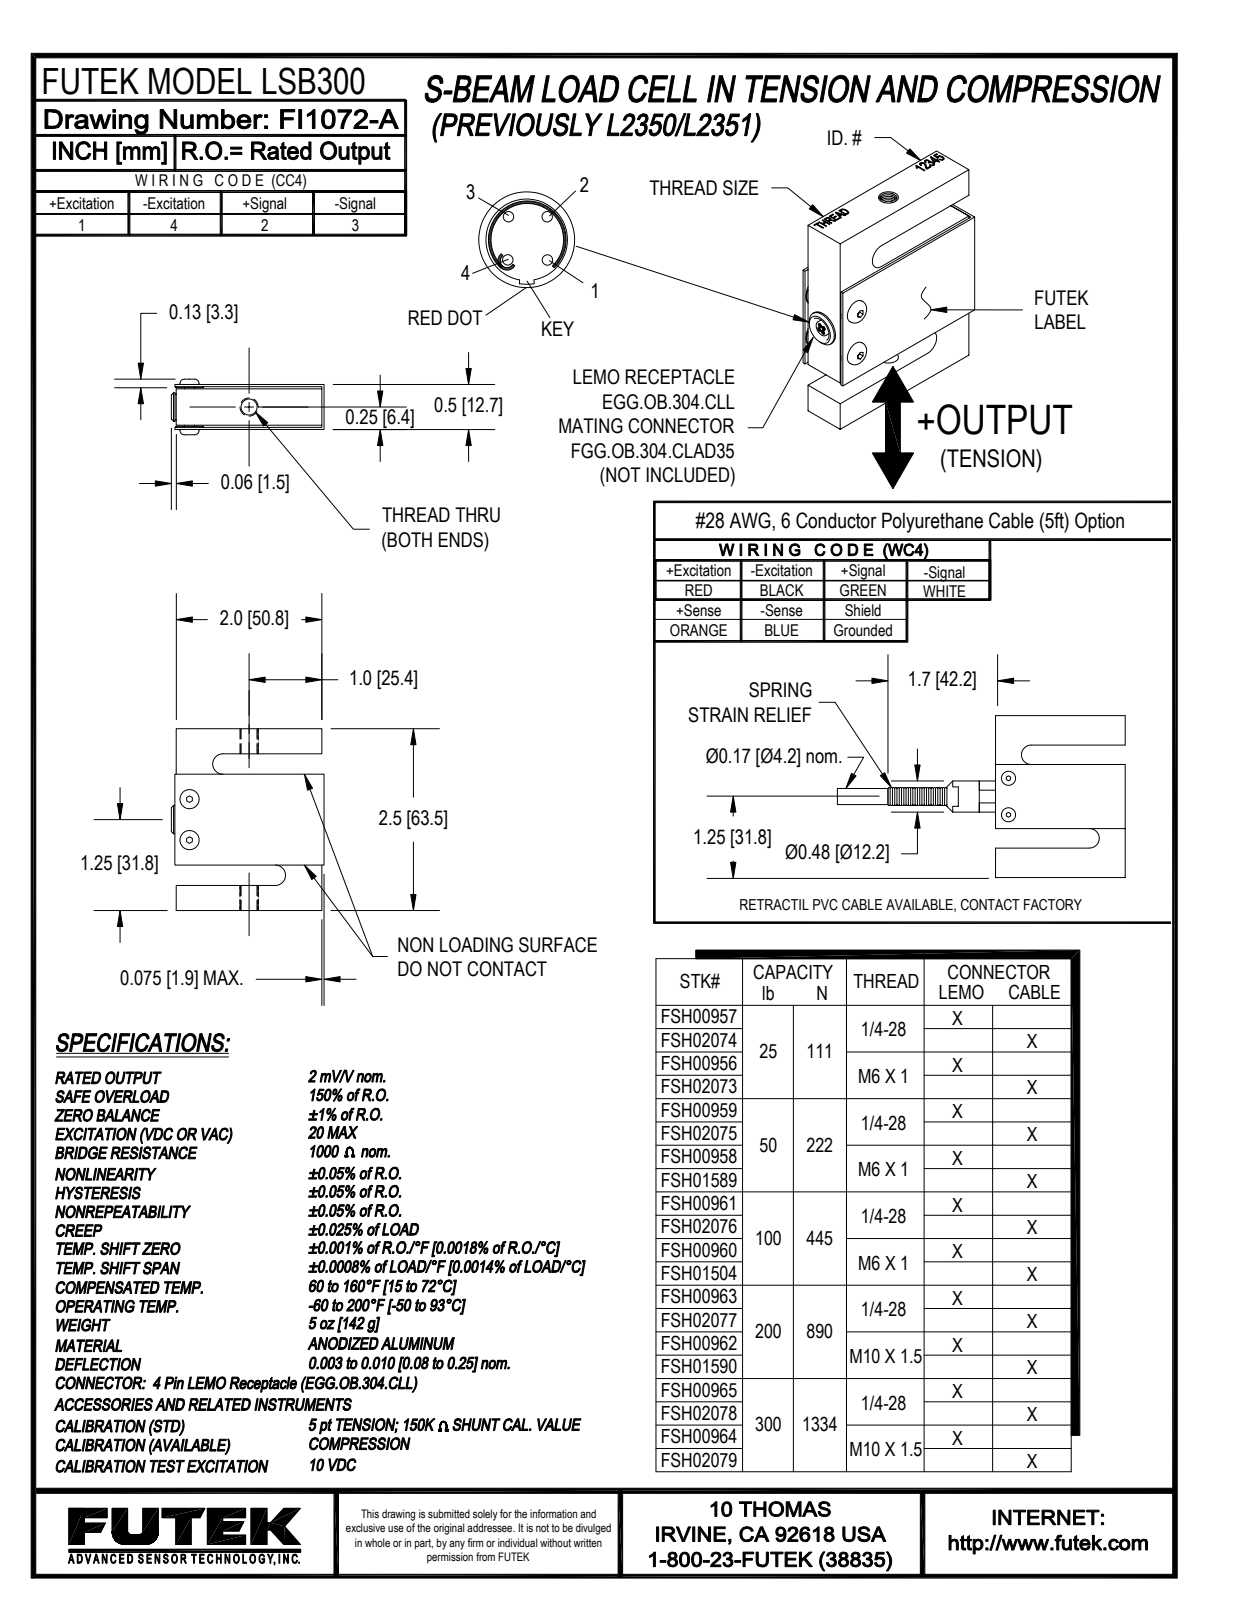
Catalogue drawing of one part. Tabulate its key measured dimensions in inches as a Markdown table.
| quantity | value |
| --- | --- |
| part name | LSB300 1-4-28 Thread Cable; ~~~PART1 |
| STEP written by | Autodesk Inventor 2008 (AUTOMOTIVE_DESIGN) |
| units | inches |
| bodies | 2 solids, 219 faces (91 planar, 40 cylindrical, 88 other) |
| overall size | 4.779 × 2.5 × 0.766 |
| volume | 2.42 in³ |
| surface area | 33.59 in² |
| round holes (diameter × count) | 0.114 × 2, 0.149 × 2, 0.17 × 2, 0.2 × 1, 0.22 × 1, 0.29 × 1, 0.32 × 1, 0.331 × 1, 0.391 × 1 |
| round bosses / shafts (diameter × count) | 0.375 × 2, 0.262 × 2, 0.138 × 2, 0.48 × 1, 0.315 × 1 |
| partial cylindrical surfaces (radius × count) | 0.14 × 2 |
| main face-to-face distances | 0.5, 0.562, 0.062, 0.058, 0.558, 0.62, 0.032, 0.532, 0.59, 0.03 |
| hole center spacings | 0.562 |
